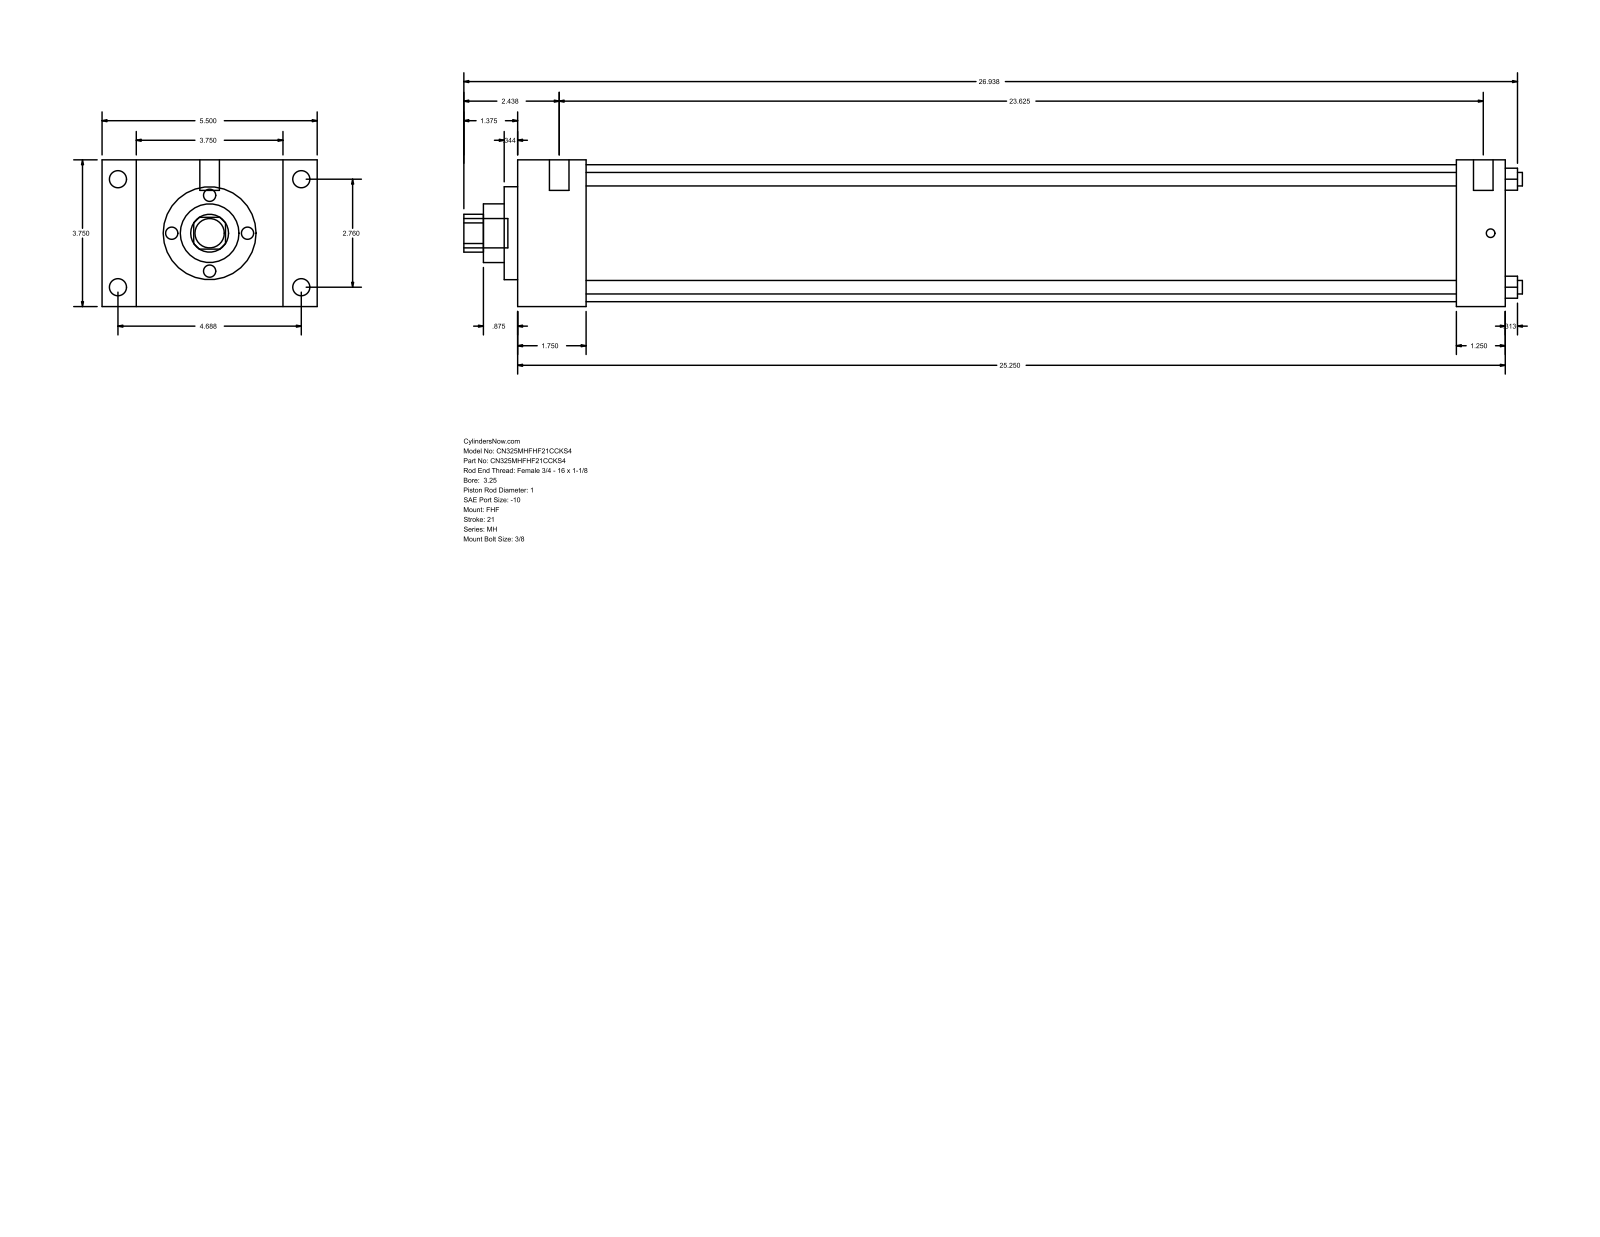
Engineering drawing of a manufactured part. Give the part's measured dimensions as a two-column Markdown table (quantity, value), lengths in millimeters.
| quantity | value |
| --- | --- |
| part name | MH_FHF__0325_1 |
| STEP written by | GSSL Pune (CONFIG_CONTROL_DESIGN) |
| units | millimeters |
| bodies | 0 solids, 90 faces (61 planar, 29 cylindrical, 0 other) |
| overall size | 687.39 × 139.7 × 95.25 |
| round holes (diameter × count) | 8.76 × 4, 25.4 × 1, 38.1 × 1, 60.33 × 1, 88.9 × 1 |
| round bosses / shafts (diameter × count) | 11.13 × 4, 5.56 × 4, 12.7 × 2, 19.05 × 1 |
| partial cylindrical surfaces (radius × count) | 12.29 × 1 |
| main face-to-face distances | 95.24, 641.35, 44.46, 596.89, 22.23, 117.47, 139.7, 609.6, 565.14, 31.75 |
| hole center spacings | 49.57, 70.1, 99.14 |
